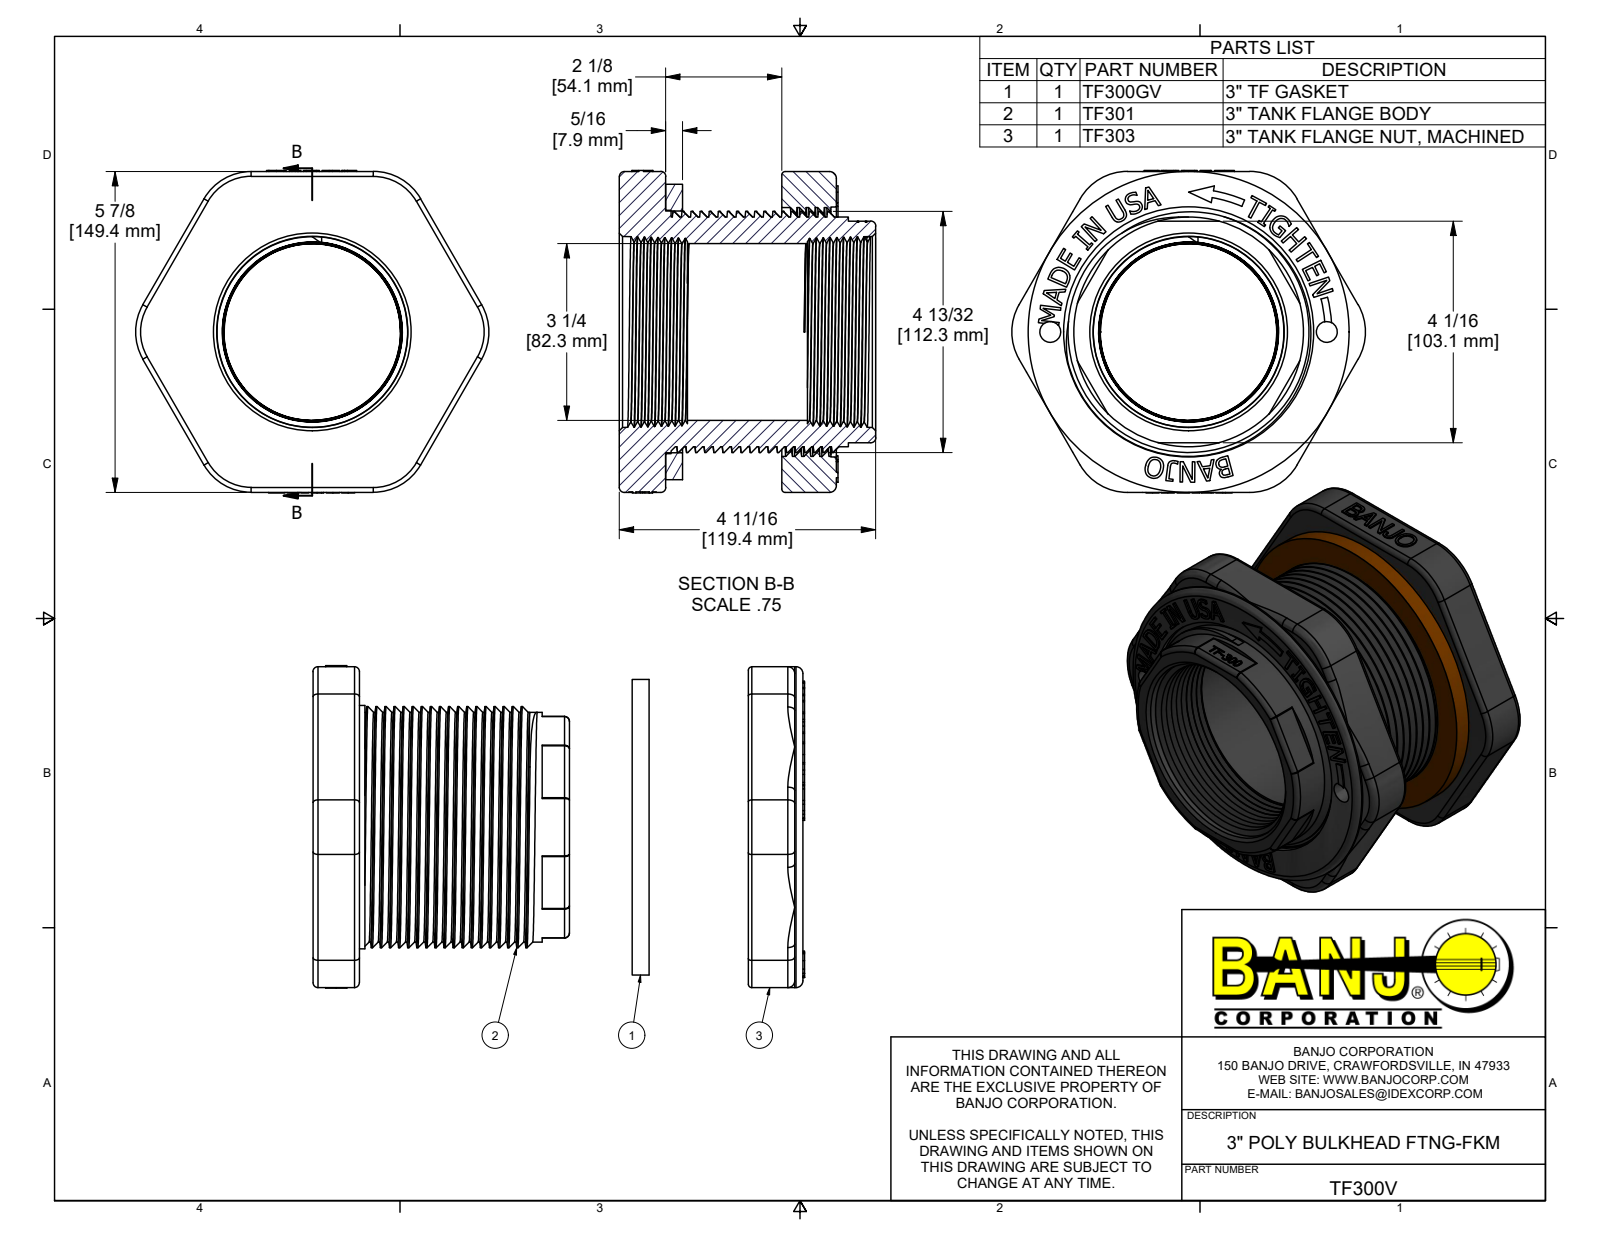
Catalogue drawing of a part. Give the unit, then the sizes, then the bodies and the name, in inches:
Units: inches
Overall size (bounding box): 6.48 × 5.91 × 4.7
Round holes (diameter × count): ⌀0.38 ×2, ⌀3.24 ×1, ⌀4.361 ×1, ⌀4.43 ×1, ⌀4.561 ×1, ⌀4.58 ×1
Round bosses / shafts (diameter × count): ⌀5.88 ×1, ⌀5.416 ×1, ⌀4.46 ×1, ⌀4.42 ×1, ⌀4.21 ×1
Partial cylindrical surfaces — rounded edges, fillets, slot ends (radius × count): R0.09 ×18, R0.06 ×12, R0.062 ×6, R0.125 ×6, R1 ×6, R1.24 ×1, R2 ×1, R2.5 ×1
Main face-to-face distances: 0.85, 2.98, 2.13, 1.16, 0.31, 1.82, 3.98, 3.13, 2.82, 1
Hole centre spacings: 2.535, 5.07
Volume: 49.08 in³ · Surface area: 313.2 in²
Bodies: 3 solids, 824 faces (407 planar, 129 cylindrical, 288 other)
Part name (STEP PRODUCT): TF300V; TF301; TF303; TF303X (+1 more)
STEP written by: Autodesk Inventor 2019 (AUTOMOTIVE_DESIGN)
